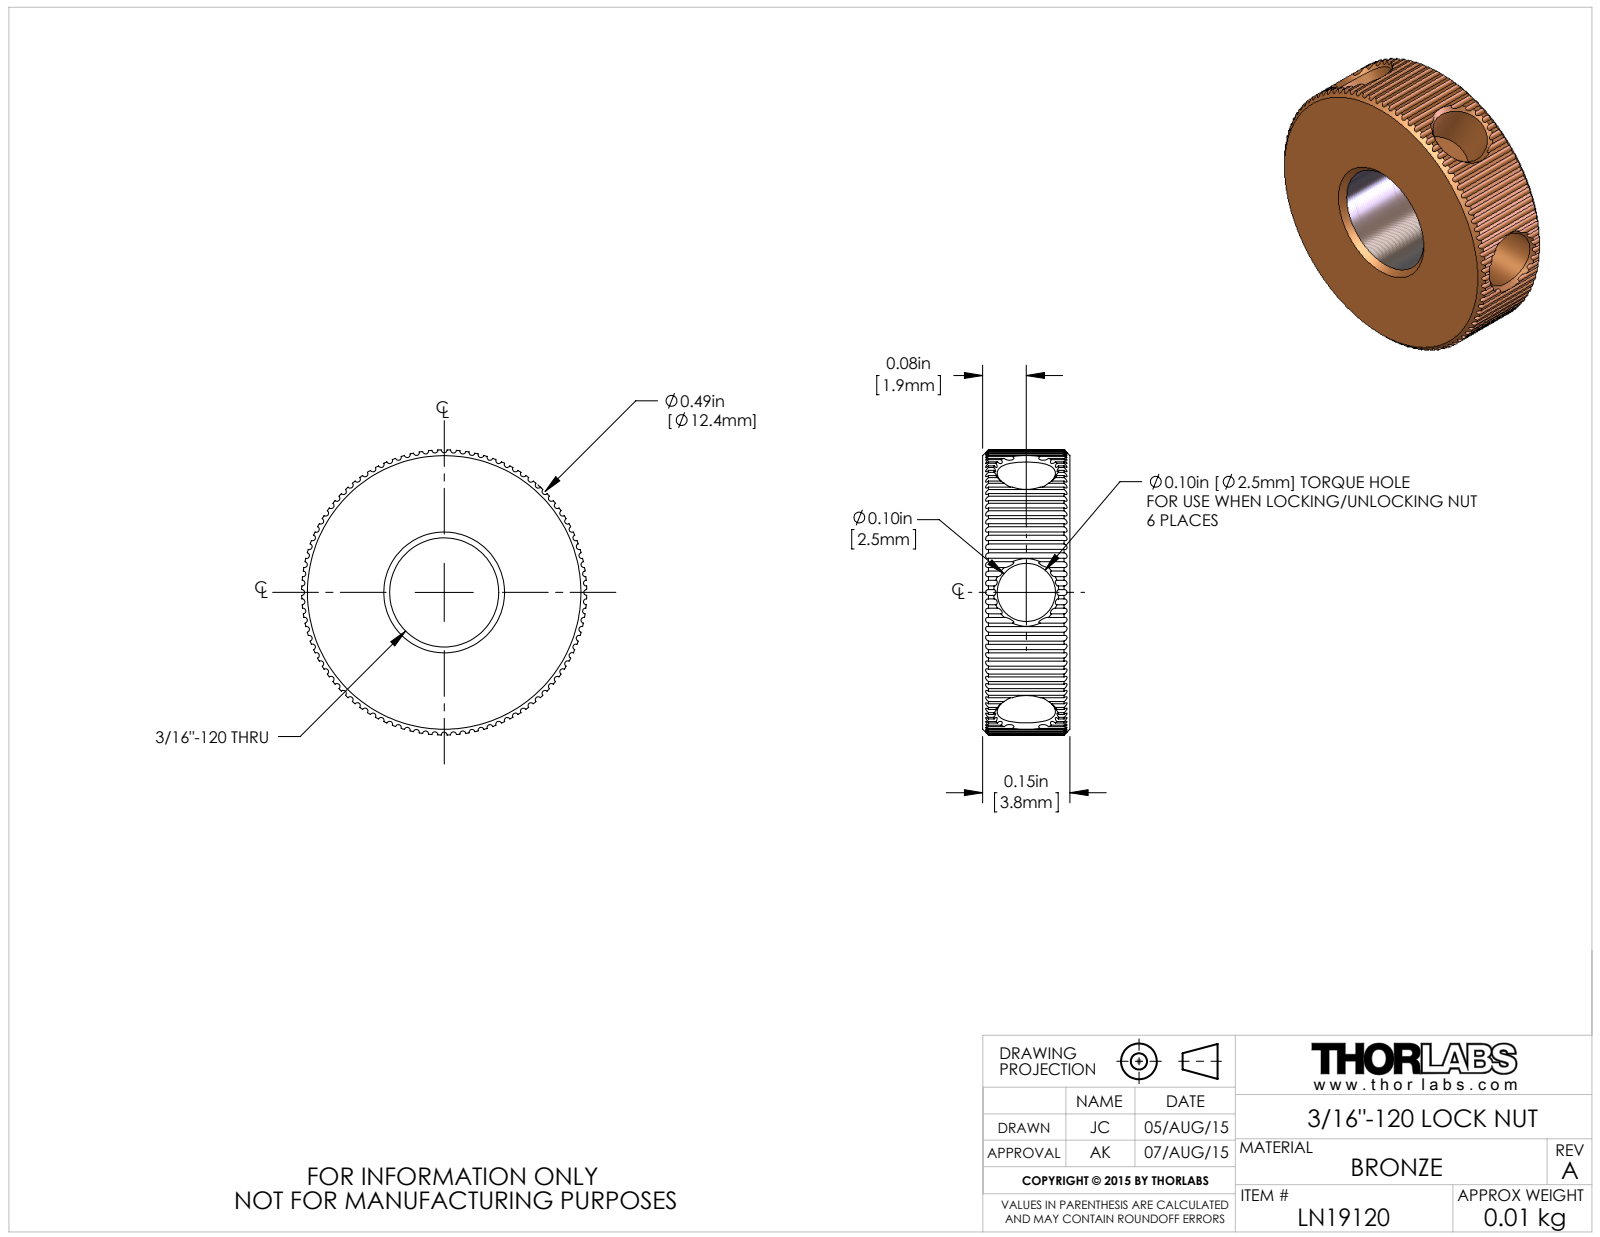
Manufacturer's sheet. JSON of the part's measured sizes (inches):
{"part_name": "TTN045710-E0W", "step_written_by": "SolidWorks 2014 (AUTOMOTIVE_DESIGN)", "units": "inches", "bodies": {"solids": 1, "faces": 380, "planar": 8, "cylindrical": 352, "other": 20}, "overall_size": [0.49, 0.49, 0.15], "volume_in3": 0.019, "surface_area_in2": 0.836, "round_holes": [[0.1, 3], [0.187, 1]], "partial_cylinders_radius": [[0.005, 96], [0.245, 1]], "face_to_face_distances": [0.15, 0.29, 0.29]}
